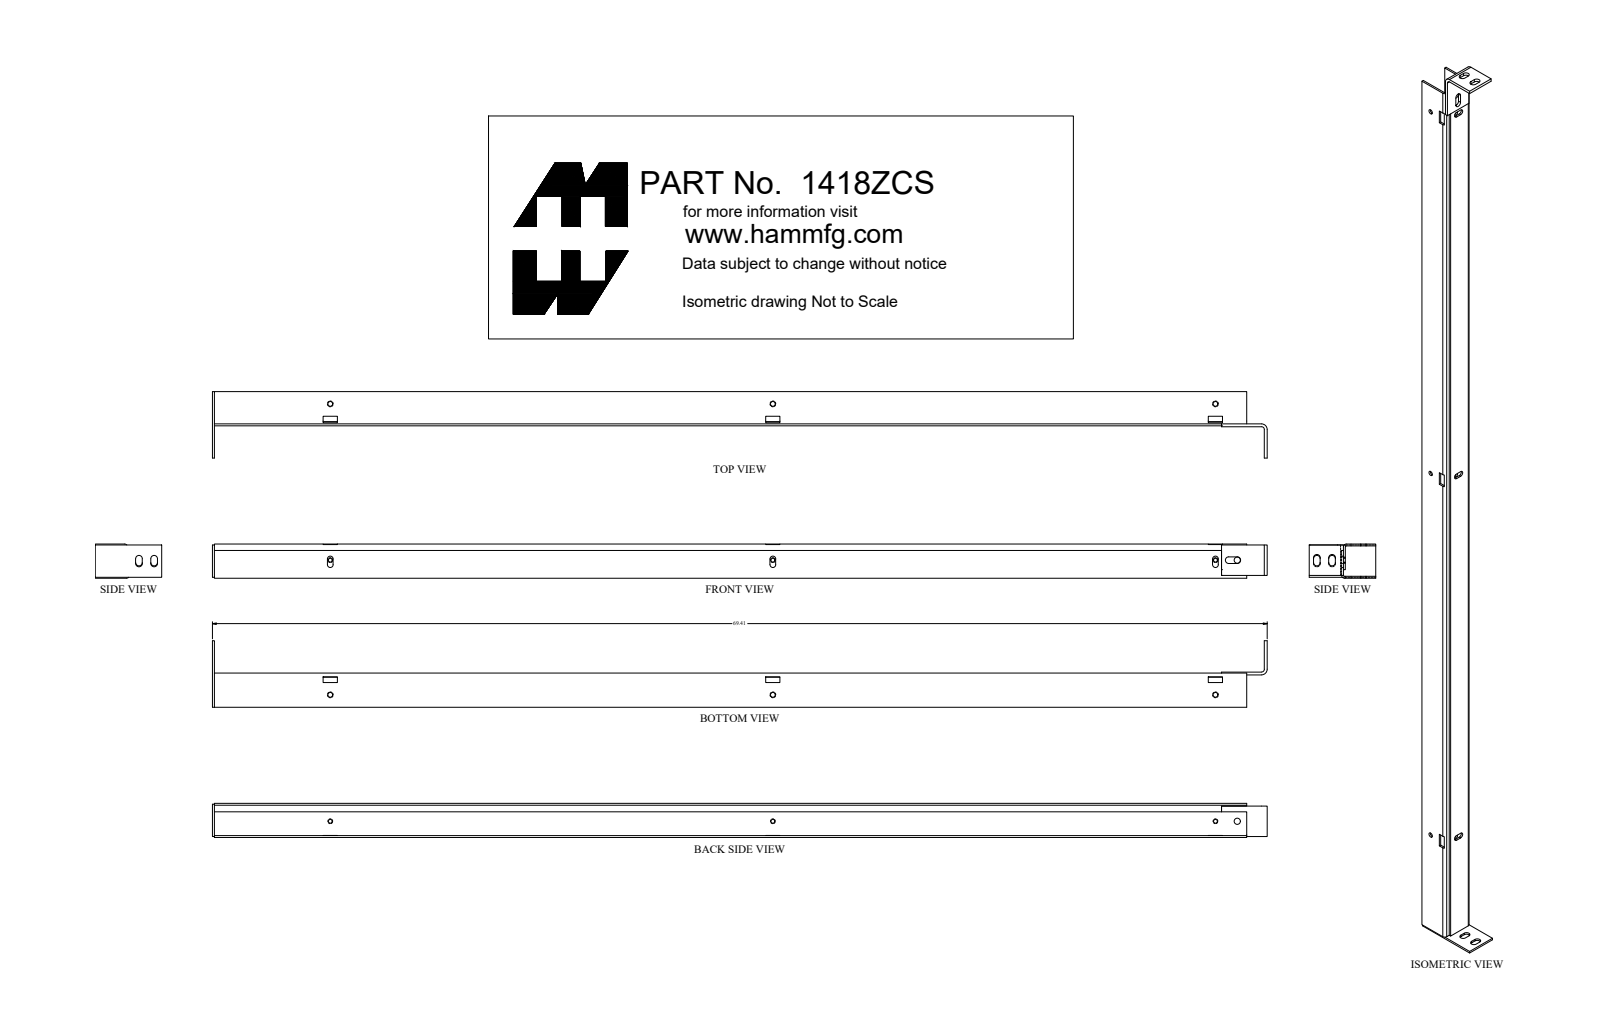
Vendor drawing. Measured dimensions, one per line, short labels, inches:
name: 1418ZCS_Default
written by: SolidWorks 2019 (CONFIG_CONTROL_DESIGN)
unit: in
bodies: 4 solids, 120 faces (72 planar, 48 cylindrical, 0 other)
size: 69.438 × 4.375 × 2.248
volume: 65.41 in³; area: 1 091 in²
holes: 3× ⌀0.283, 3× ⌀0.344, 1× ⌀0.406
rounds: 8× R0.219, 3× R0.06, 3× R0.185, 3× R0.187, 3× R0.188, 2× R0.25
face distances: 0.125, 0.125, 2.248, 2.123, 2.123, 1.998, 0.25, 2.125, 2, 2.25
hole spacings: 29.125, 29.125, 58.25, 1.438, 30.563, 59.688
